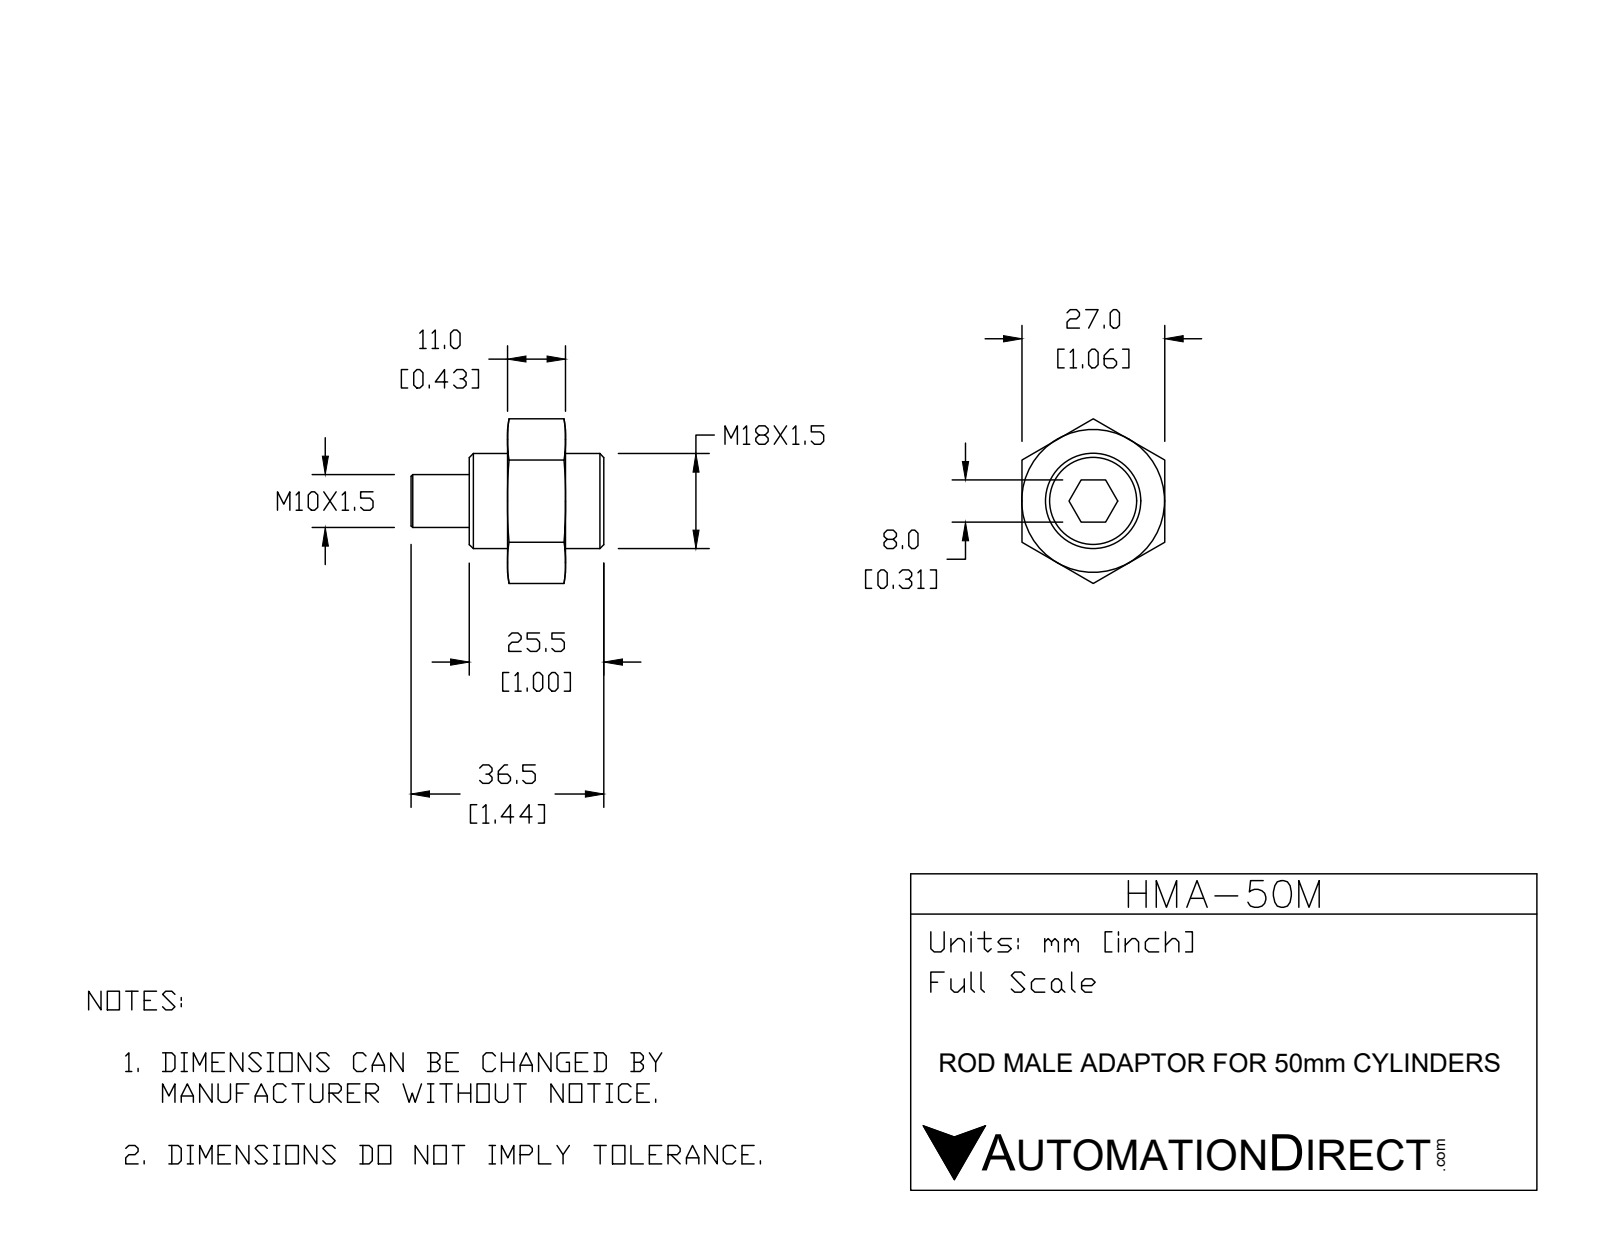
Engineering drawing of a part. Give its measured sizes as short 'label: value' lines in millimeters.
name: HMA-50M
written by: SolidWorks 2015 (CONFIG_CONTROL_DESIGN)
unit: mm
bodies: 2 solids, 44 faces (18 planar, 6 cylindrical, 20 other)
size: 36.5 × 31.18 × 27
volume: 10 955 mm³; area: 4 874 mm²
holes: 1× ⌀18
bosses: 1× ⌀10
face distances: 27, 11, 18.25, 7.25, 25.5, 8, 36.5, 29.25, 9, 1.75
